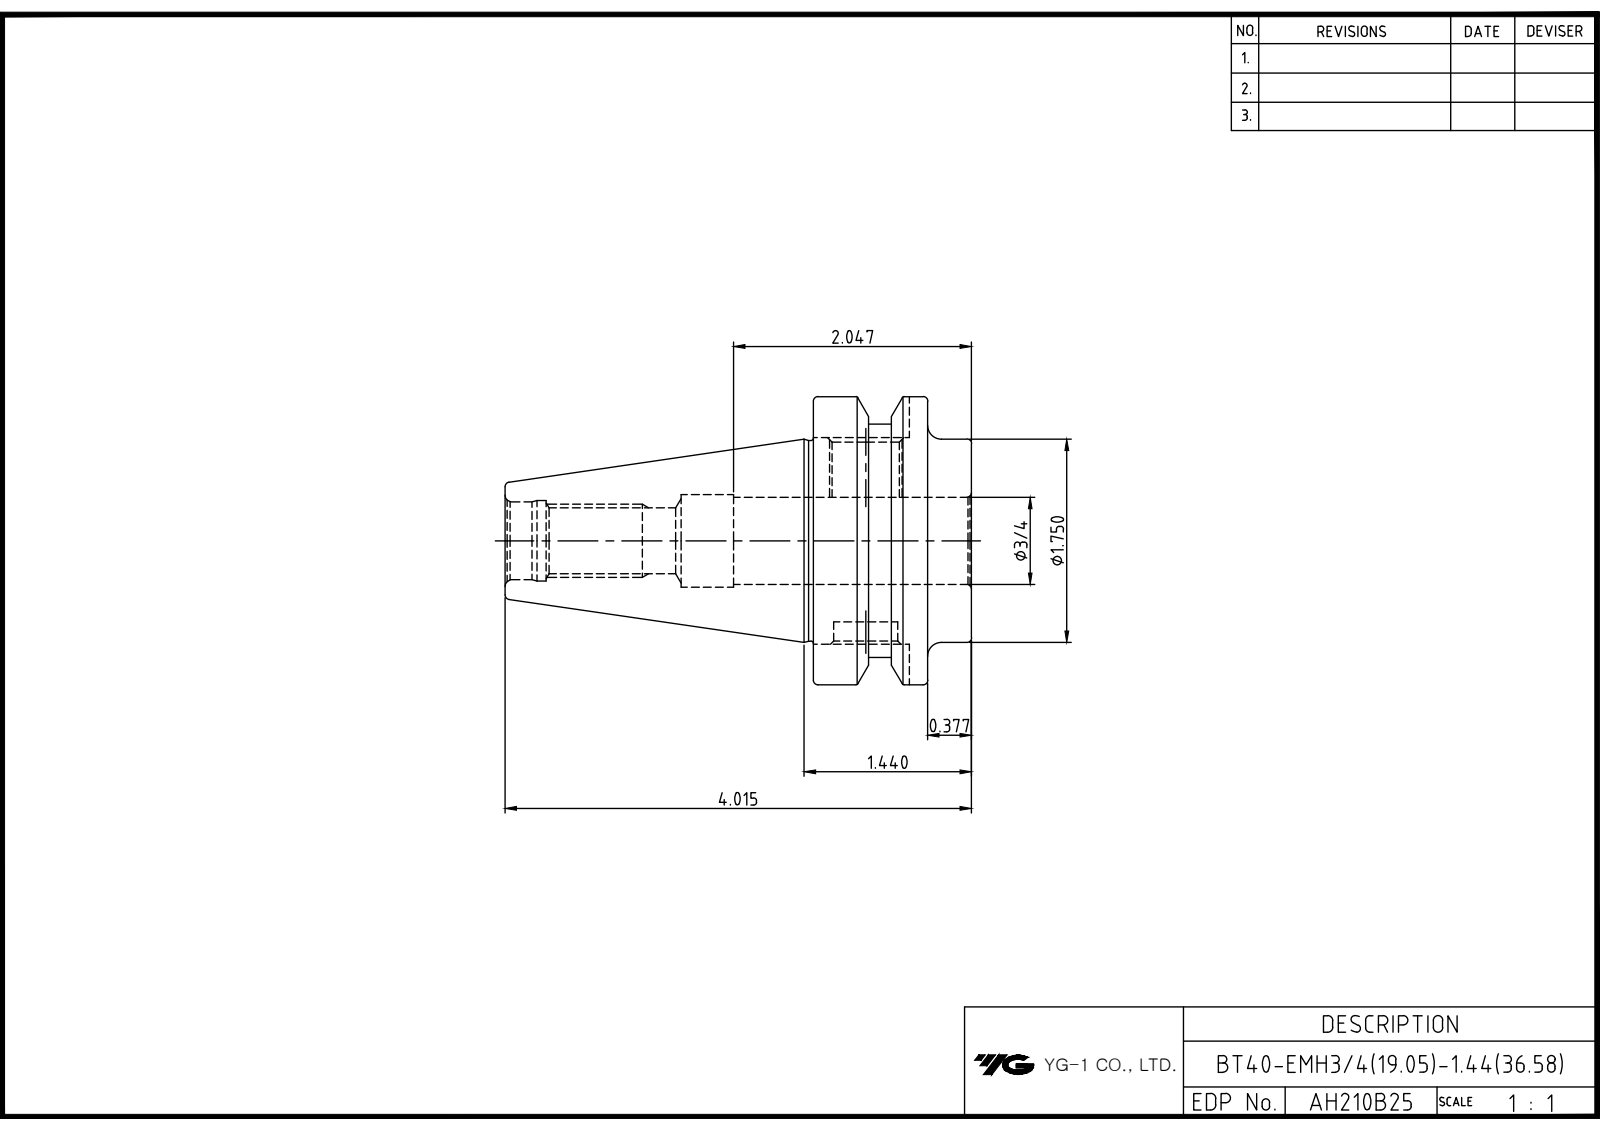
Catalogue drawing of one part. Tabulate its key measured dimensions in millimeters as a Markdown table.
| quantity | value |
| --- | --- |
| part name | LO-BT40-EMH19.05-36.58 |
| STEP written by | Autodesk Inventor 2022 (AUTOMOTIVE_DESIGN) |
| units | millimeters |
| bodies | 1 solid, 51 faces (18 planar, 16 cylindrical, 17 other) |
| overall size | 101.98 × 63 × 63 |
| volume | 120 516 mm³ |
| surface area | 25 771 mm² |
| round holes (diameter × count) | 13.84 × 1, 14 × 1, 14.35 × 1, 17 × 1, 17.6 × 1, 19.05 × 1, 20.25 × 1 |
| round bosses / shafts (diameter × count) | 63 × 1, 51 × 1, 44.45 × 1, 44 × 1 |
| partial cylindrical surfaces (radius × count) | 8.05 × 1 |
| main face-to-face distances | 34.58, 25, 9.58, 17.1, 7.9, 17.48, 12.1, 5, 12.9, 22.48 |
